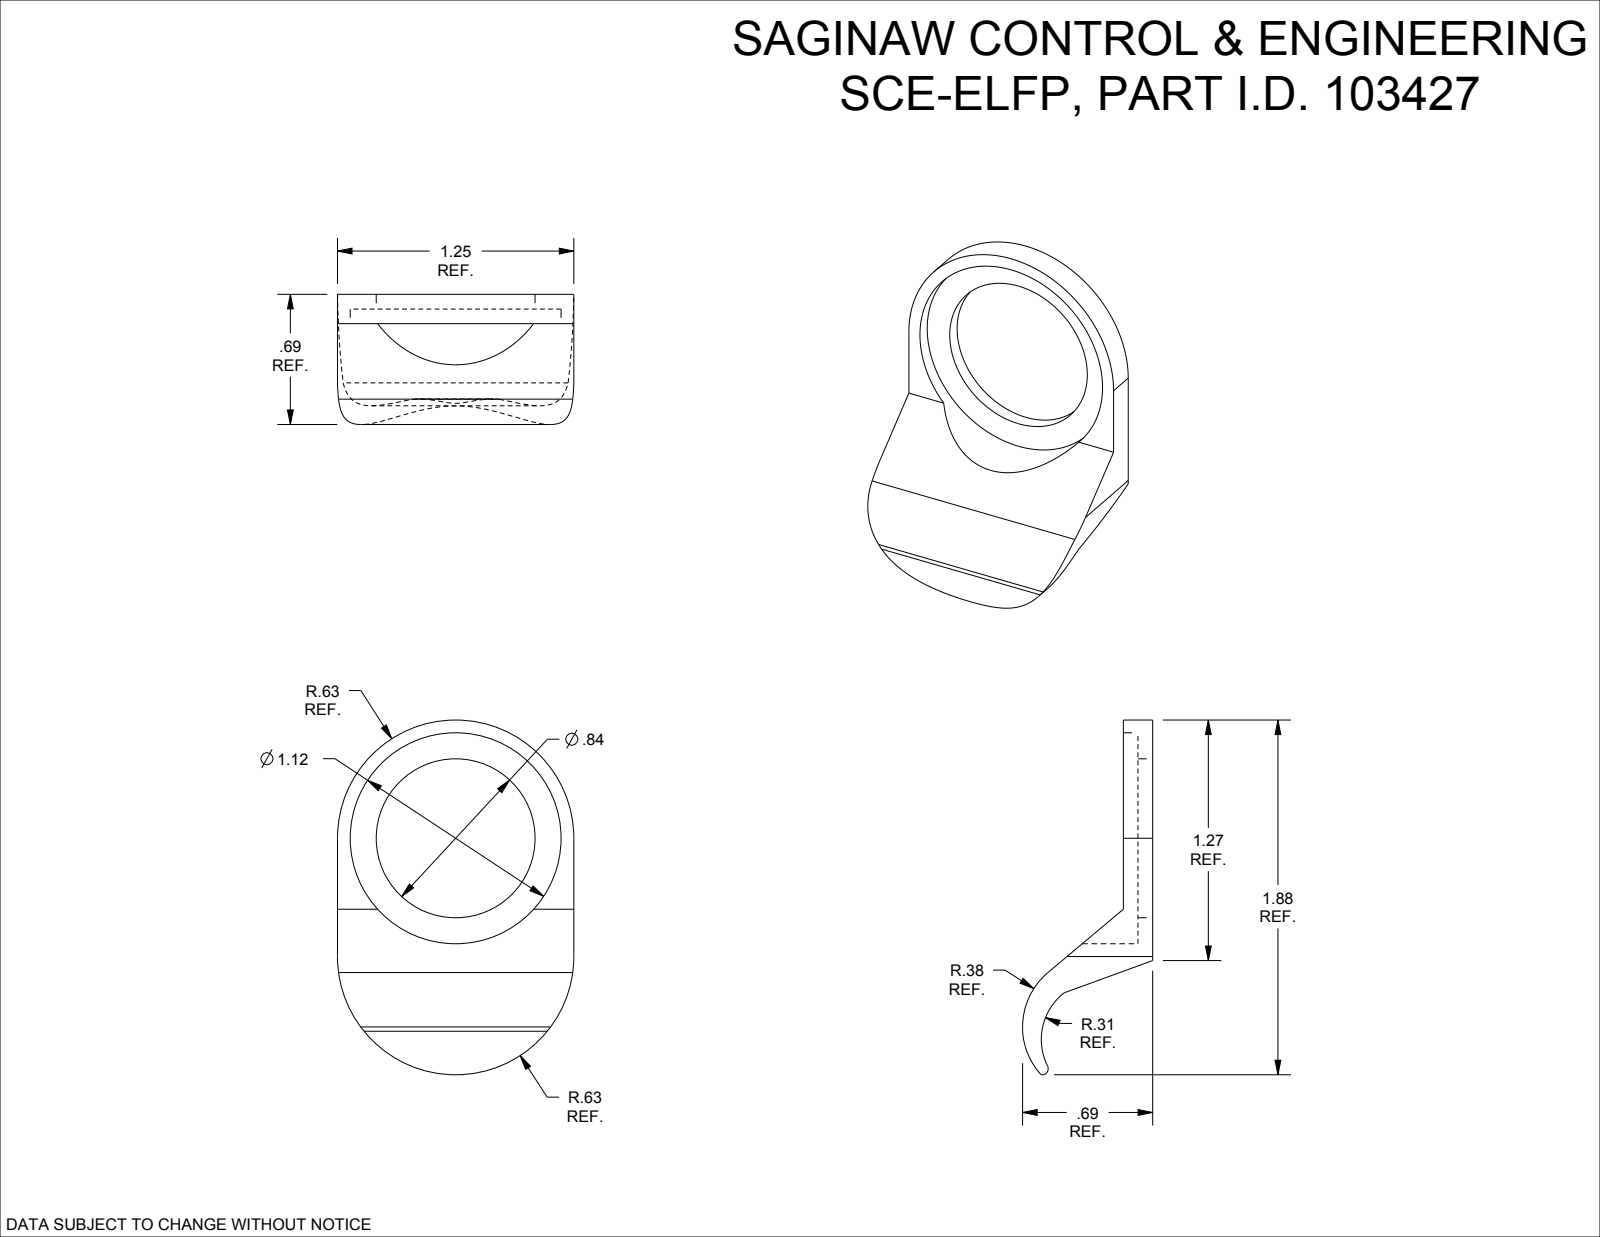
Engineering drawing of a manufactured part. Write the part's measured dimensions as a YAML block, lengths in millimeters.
part_name: "SCE-ELFP"
step_written_by: "SolidWorks 2019 (AUTOMOTIVE_DESIGN)"
units: millimeters
bodies: {solids: 1, faces: 18, planar: 8, cylindrical: 10, other: 0}
overall_size: [47.6, 31.8, 17.5]
volume: 4280
surface_area: 3254
round_holes:
  - {diameter: 21.3, count: 1}
  - {diameter: 28.3, count: 1}
partial_cylinders:
  - {radius: 9.5, count: 2}
  - {radius: 15.9, count: 2}
  - {radius: 0.9, count: 1}
  - {radius: 7.9, count: 1}
face_to_face_distances: [2, 3.9, 2, 31.8, 17.5, 15.5, 13.5]
